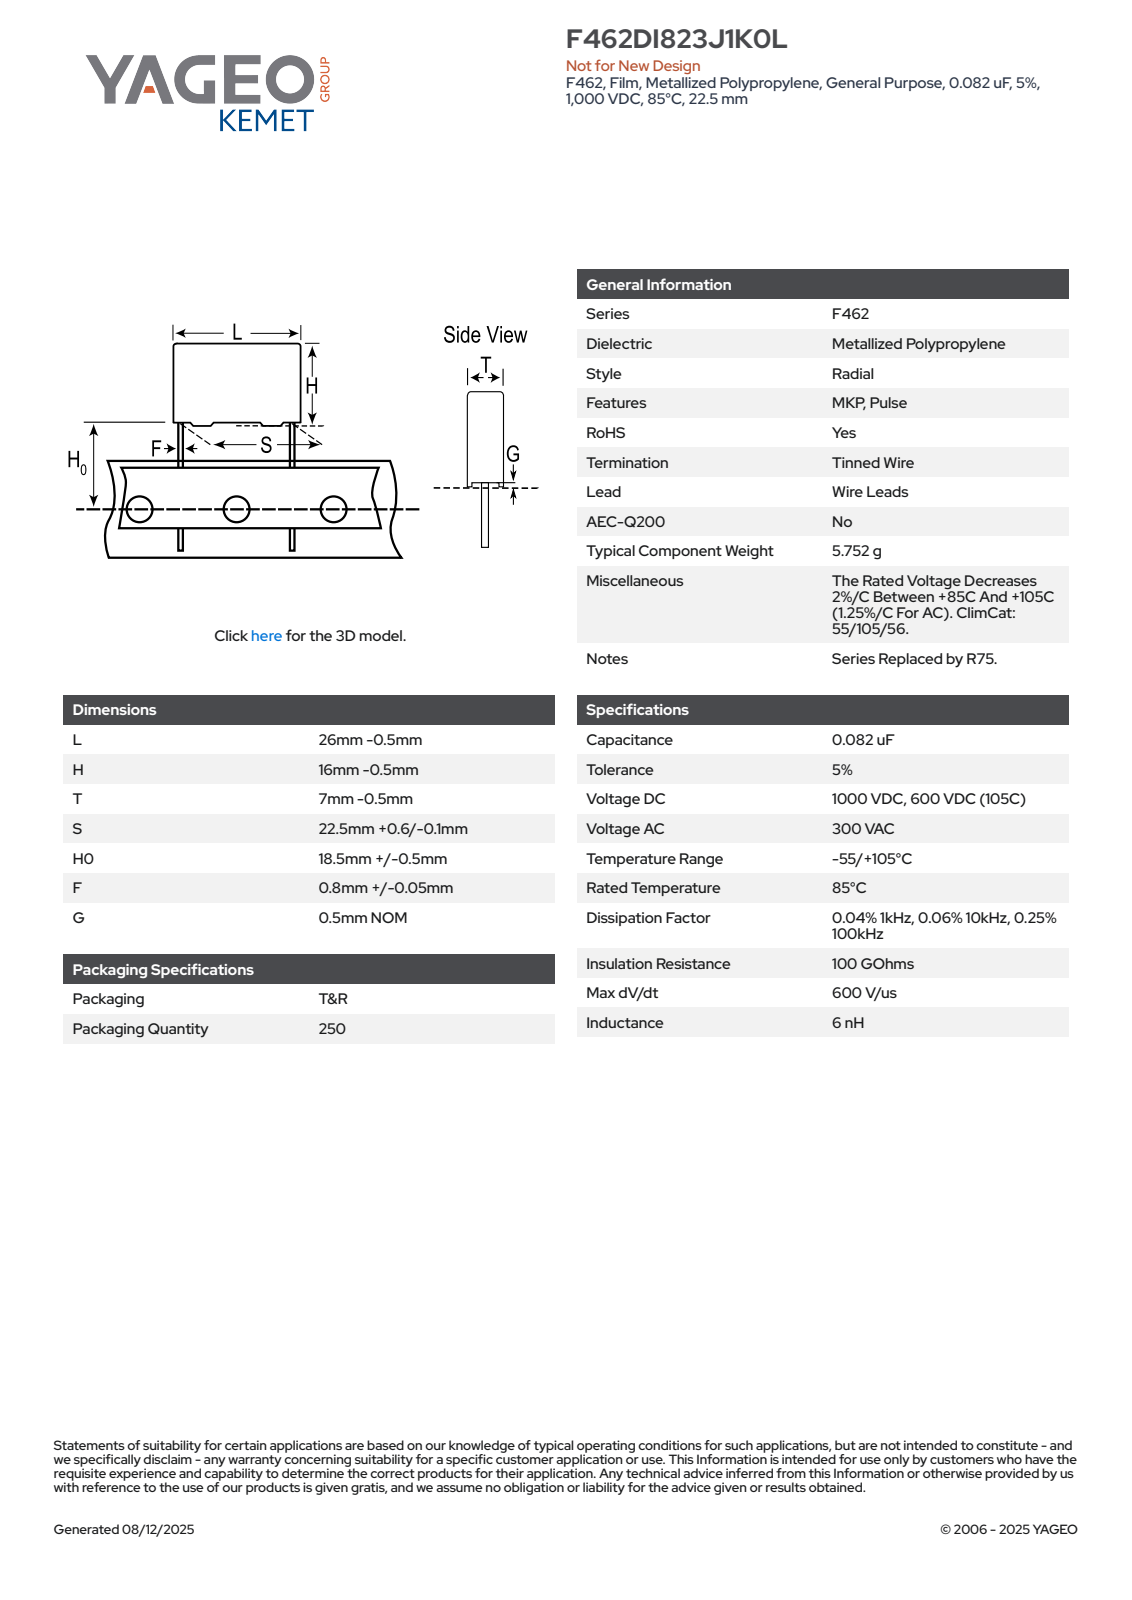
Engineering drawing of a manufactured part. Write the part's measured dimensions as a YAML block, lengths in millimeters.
part_name: "CFR_RBG_26X16X7_L25.5H15.5T6.5S22.5H019F0.85G0.5"
step_written_by: "SolidWorks 2014 (AUTOMOTIVE_DESIGN)"
units: millimeters
bodies: {solids: 4, faces: 89, planar: 81, cylindrical: 8, other: 0}
overall_size: [34.5, 25.5, 6.5]
volume: 2508
surface_area: 1469
round_bosses_or_shafts:
  - {diameter: 0.85, count: 2}
partial_cylinders:
  - {radius: 0.5, count: 4}
face_to_face_distances: [6.5, 15, 25.5, 0.37, 6.13, 0.5, 15.5, 5.76, 19, 19.5]
